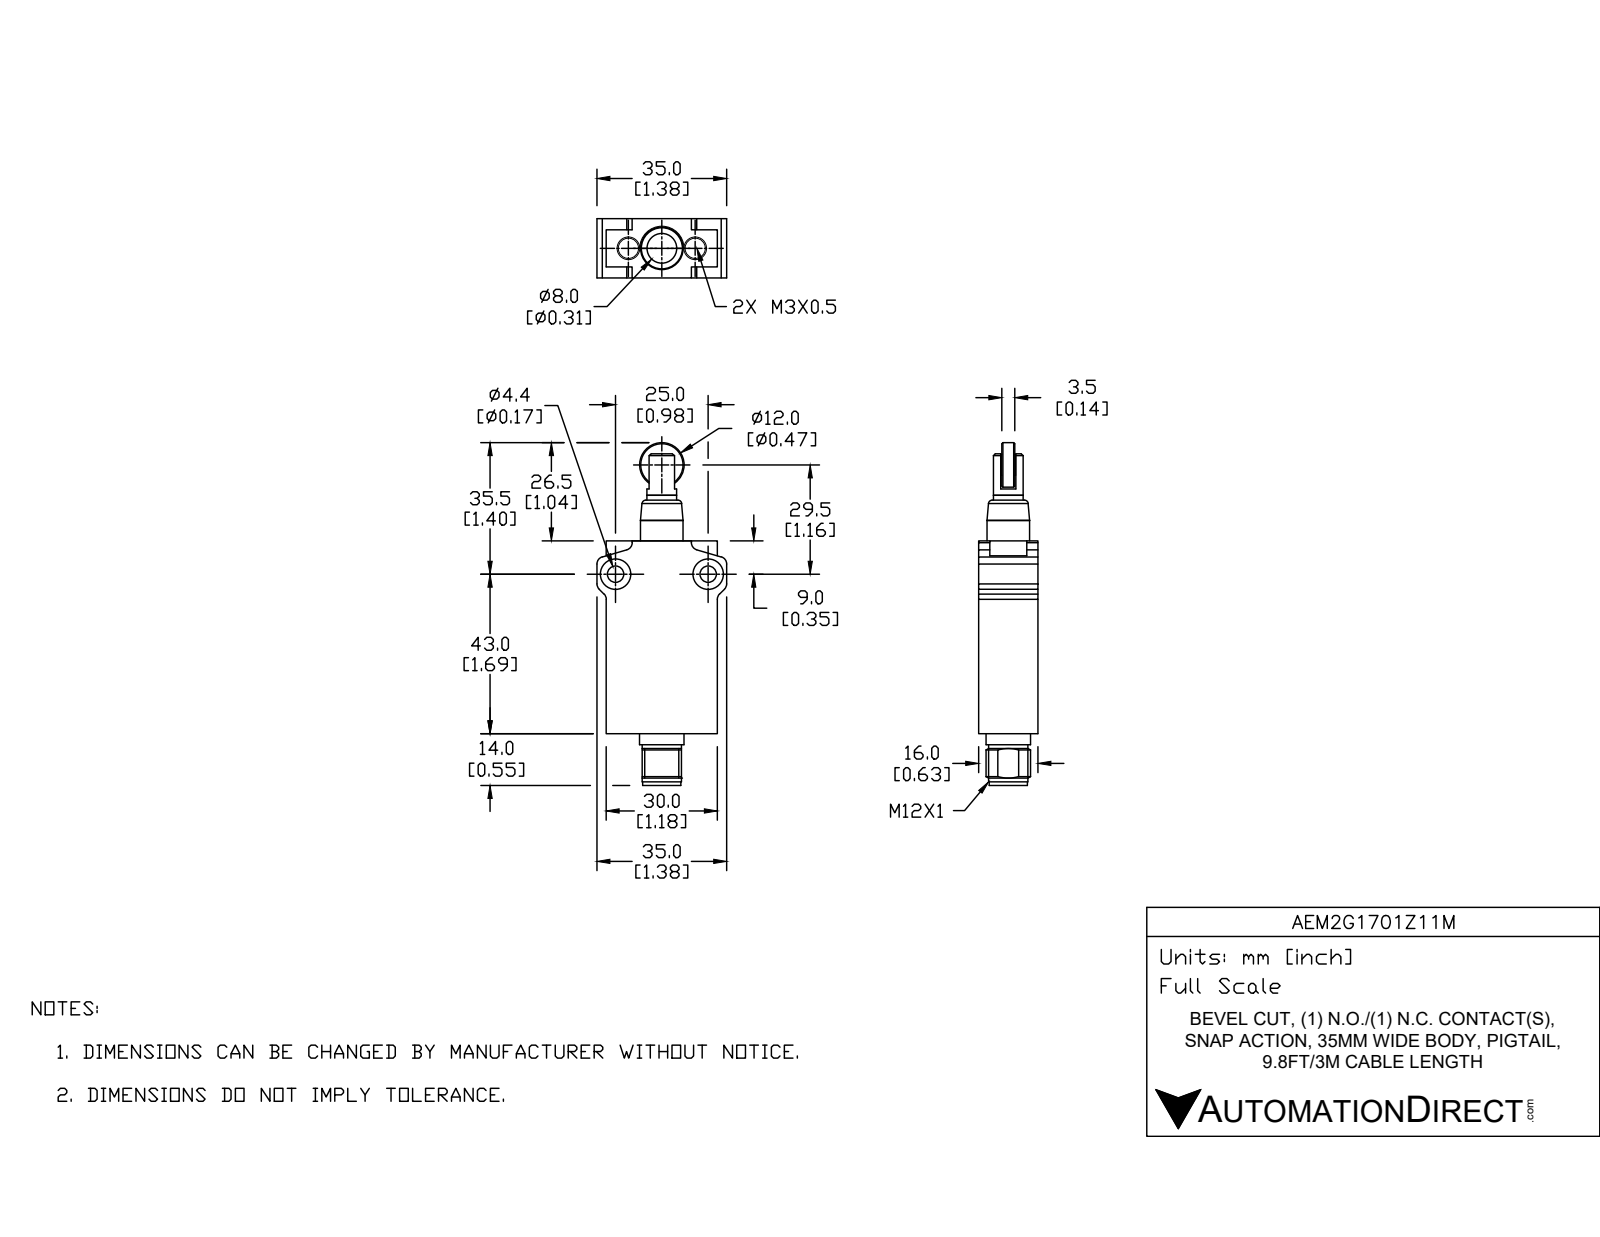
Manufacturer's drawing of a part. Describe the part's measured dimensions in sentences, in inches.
The part is named "AEM2G1701Z11M". Its 3-D file was written by "SolidWorks 2017 (AUTOMOTIVE_DESIGN)". It is 5 solids with 180 faces: 59 planar, 74 cylindrical and 47 other. Overall it measures 3.642 by 1.378 by 0.63 inches. Its volume is 1.716 cubic inches and its surface area 14.46 square inches. Round holes: 2 of diameter 0.118, 2 of diameter 0.173, 2 of diameter 0.323. Round bosses or shafts: 2 of diameter 0.472, 1 of diameter 0.453, 1 of diameter 0.417, 1 of diameter 0.406, 1 of diameter 0.315, 1 of diameter 0.236, 1 of diameter 0.22. Partial cylindrical surfaces (rounded edges, fillets, slot ends): 8 of radius 0.079, 1 of radius 0.256. The main face-to-face distances are 0.63, 1.181, 2.047, 0.472, 1.858, 0.189, 0.157, 0.234, 0.238, 0.098. The hole center spacings are 0.748, 0.984.
